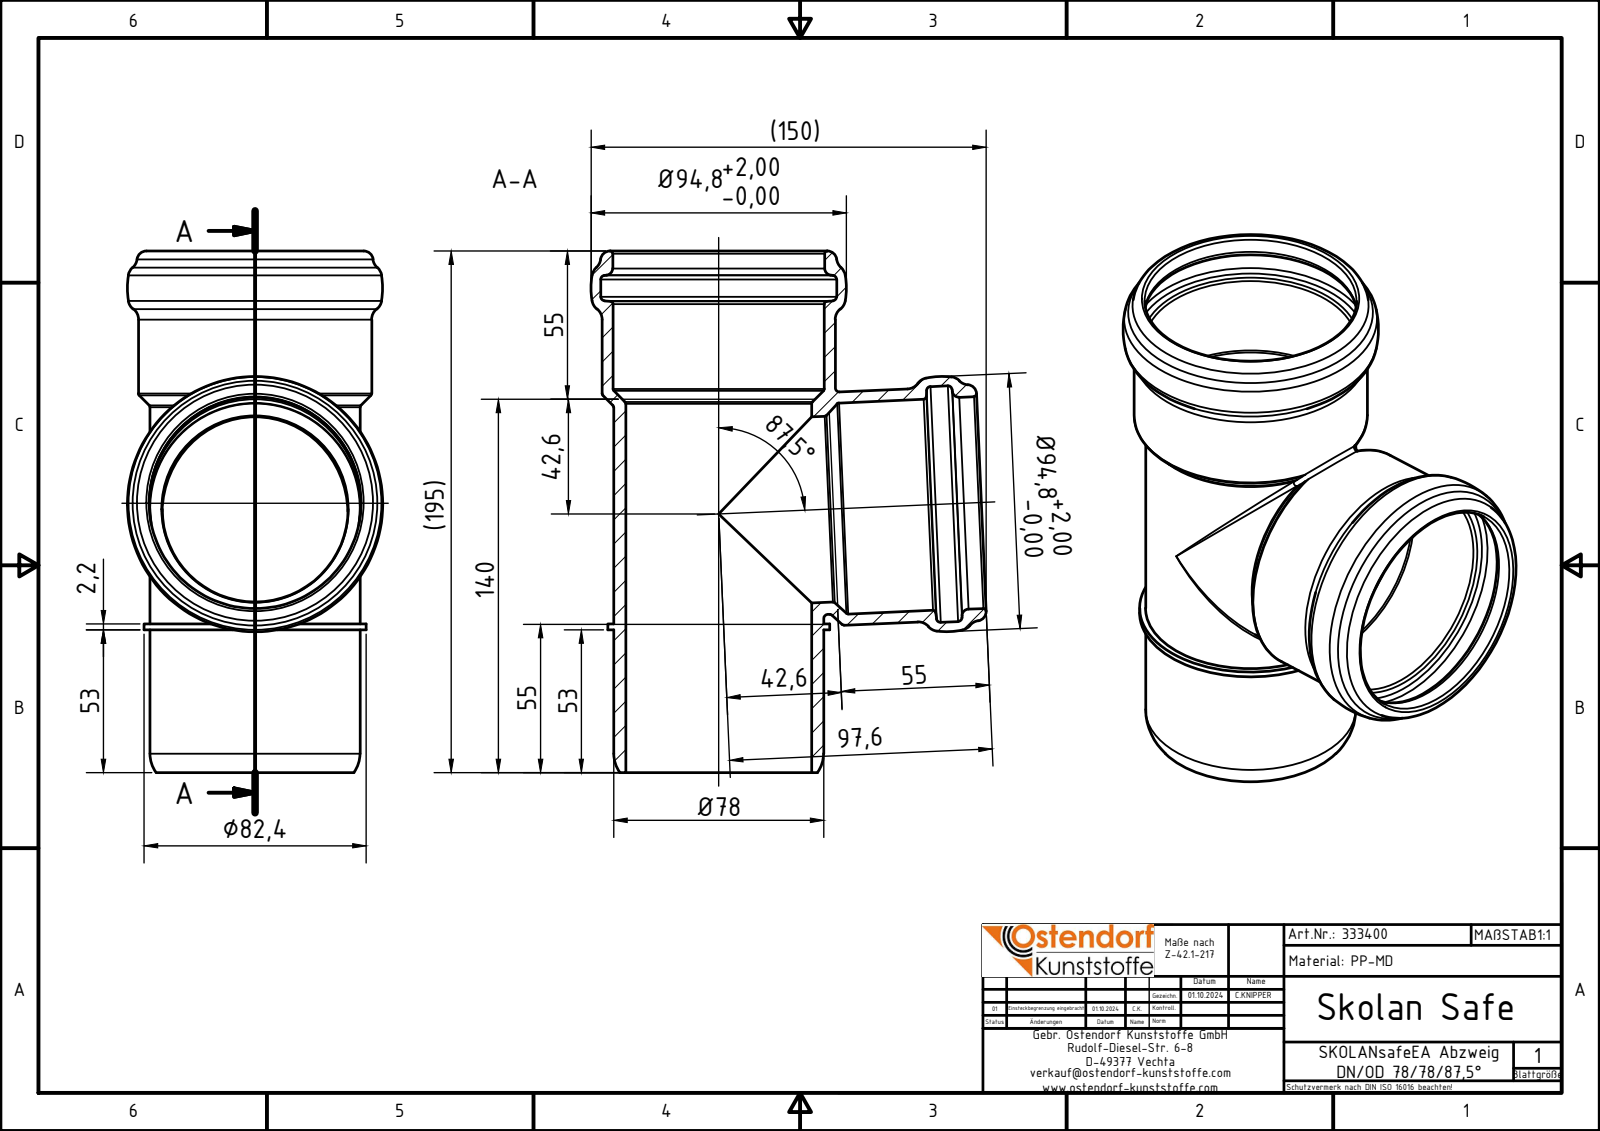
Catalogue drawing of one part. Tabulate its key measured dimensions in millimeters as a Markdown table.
| quantity | value |
| --- | --- |
| part name | 333400z |
| STEP written by | Autodesk Inventor 2024 (AUTOMOTIVE_DESIGN) |
| units | millimeters |
| bodies | 1 solid, 60 faces (3 planar, 14 cylindrical, 43 other) |
| overall size | 193.6 × 146.67 × 94.8 |
| volume | 270 027 mm³ |
| surface area | 129 078 mm² |
| round holes (diameter × count) | 69 × 2, 78.4 × 2, 78.7 × 2, 87.6 × 2 |
| round bosses / shafts (diameter × count) | 86.6 × 2, 78 × 2, 82.4 × 1 |
| main face-to-face distances | 2.2, 50.8, 53 |
